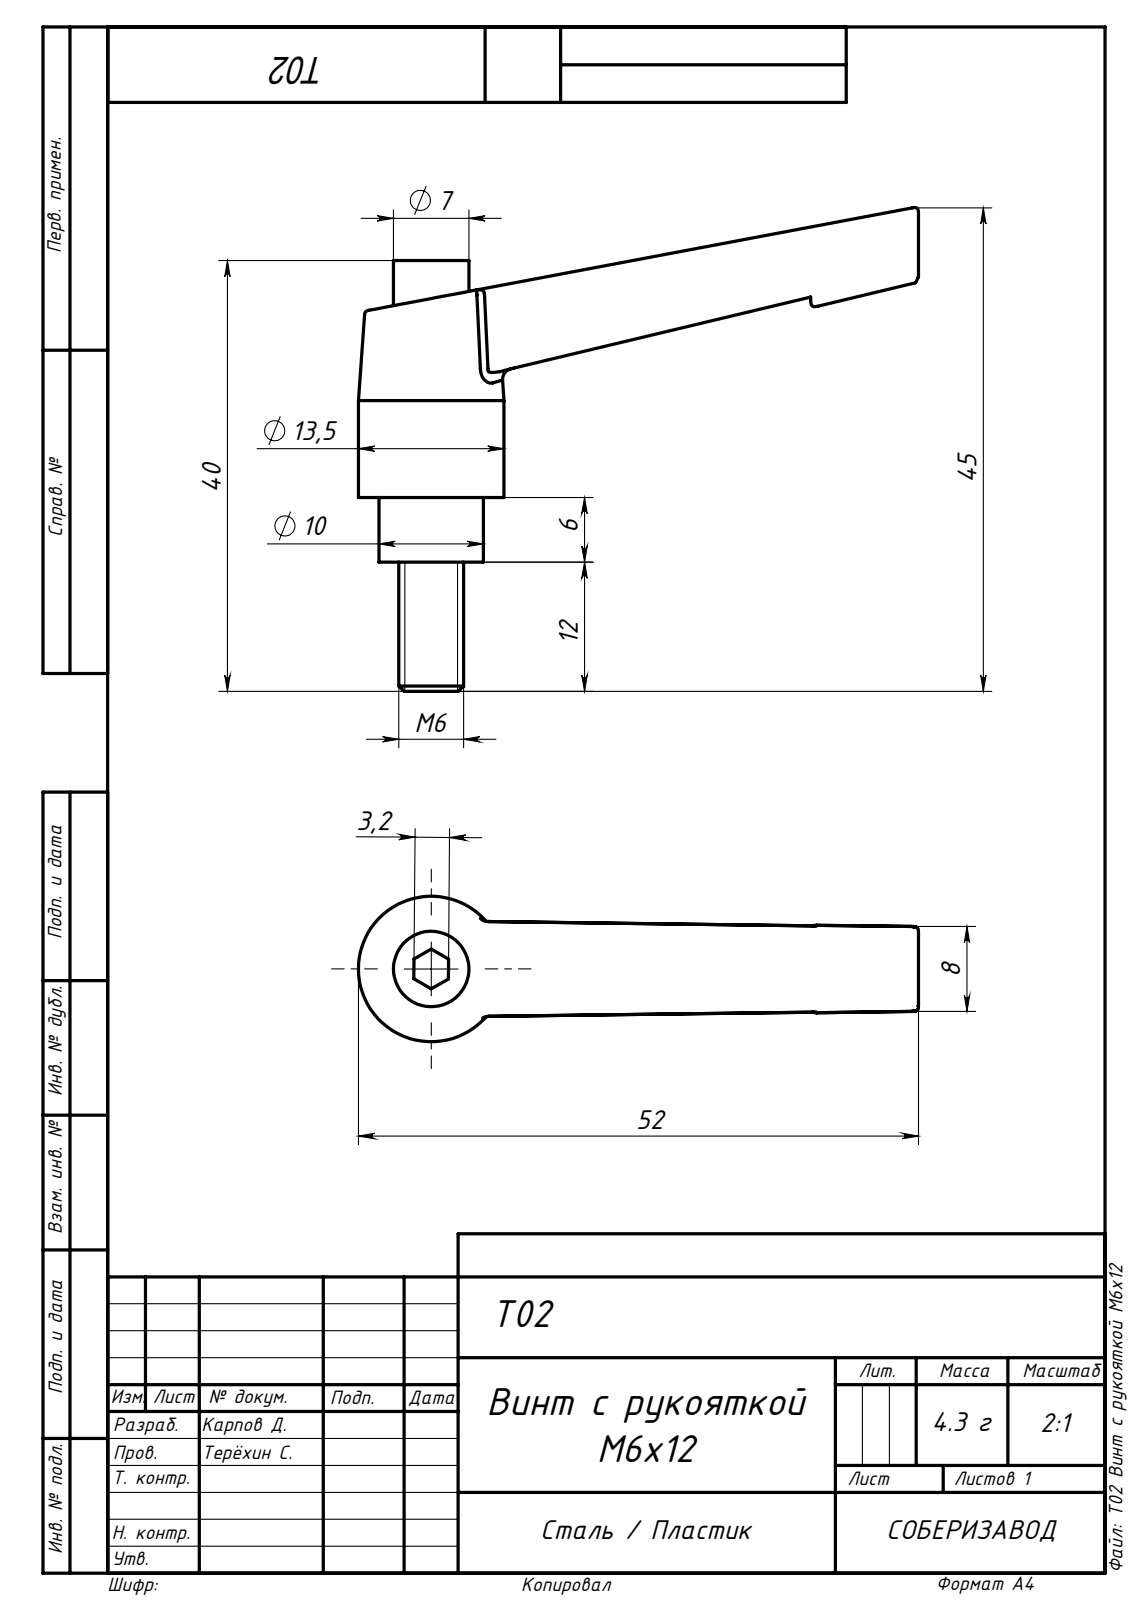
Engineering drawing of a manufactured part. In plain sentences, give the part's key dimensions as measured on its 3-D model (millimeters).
The part is named "T02 Винт с рукояткой М6х12". Its 3-D file was written by "SolidWorks 2020 (AUTOMOTIVE_DESIGN)". It is 1 solid with 73 faces: 30 planar, 8 cylindrical and 35 other. Overall it measures 51.95 by 44.91 by 13.5 millimeters. Its volume is 4 329 cubic millimeters and its surface area 3 244 square millimeters. Round bosses or shafts: 1 of diameter 13.5, 1 of diameter 9.7, 1 of diameter 7, 1 of diameter 6. The main face-to-face distances are 24.75, 6, 30.75, 9, 28.18, 8.23, 0.77, 28, 22, 2.75.
